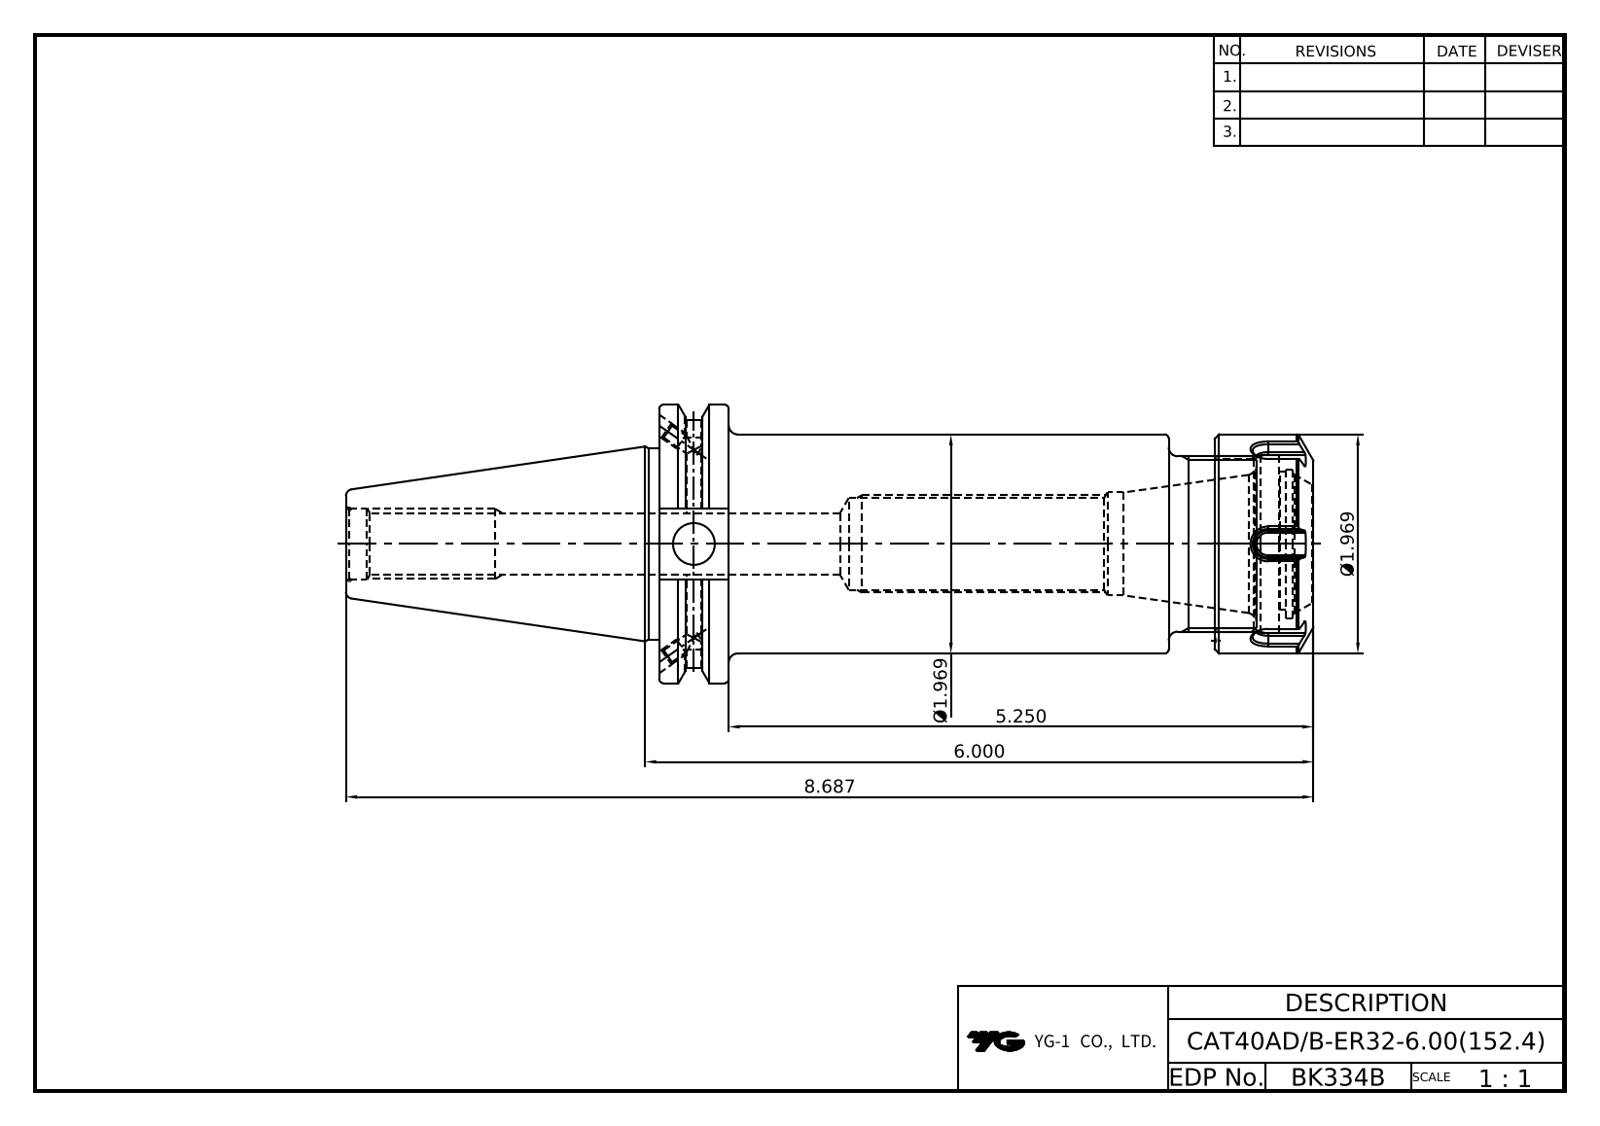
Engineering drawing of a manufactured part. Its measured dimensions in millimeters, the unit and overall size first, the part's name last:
Units: millimetres
Overall size (bounding box): 220.65 × 63.5 × 61.09
Round holes (diameter × count): ⌀3.24 ×4, ⌀4 ×2, ⌀4.2 ×2, ⌀1 ×1, ⌀9.53 ×1, ⌀13.39 ×1, ⌀16.3 ×1, ⌀20.5 ×1, ⌀23.5 ×1, ⌀27.1 ×1, ⌀31.4 ×1, ⌀33.8 ×1
Round bosses / shafts (diameter × count): ⌀63.5 ×1, ⌀50 ×1, ⌀43.6 ×1, ⌀40 ×1
Partial cylindrical surfaces — rounded edges, fillets, slot ends (radius × count): R0.5 ×12, R8.19 ×1, R28.15 ×1
Main face-to-face distances: 15.88, 116.23, 100.35, 149.23, 133.35, 33, 126.73, 110.85, 10.5, 22.5
Hole centre spacings: 0.8, 22, 22.8
Volume: 296 291 mm³ · Surface area: 55 322 mm²
Bodies: 2 solids, 167 faces (71 planar, 48 cylindrical, 48 other)
Part name (STEP PRODUCT): LO-CAT40ADB-ER32-6.00; ER32NUT
STEP written by: Autodesk Inventor 2025 (AUTOMOTIVE_DESIGN)
